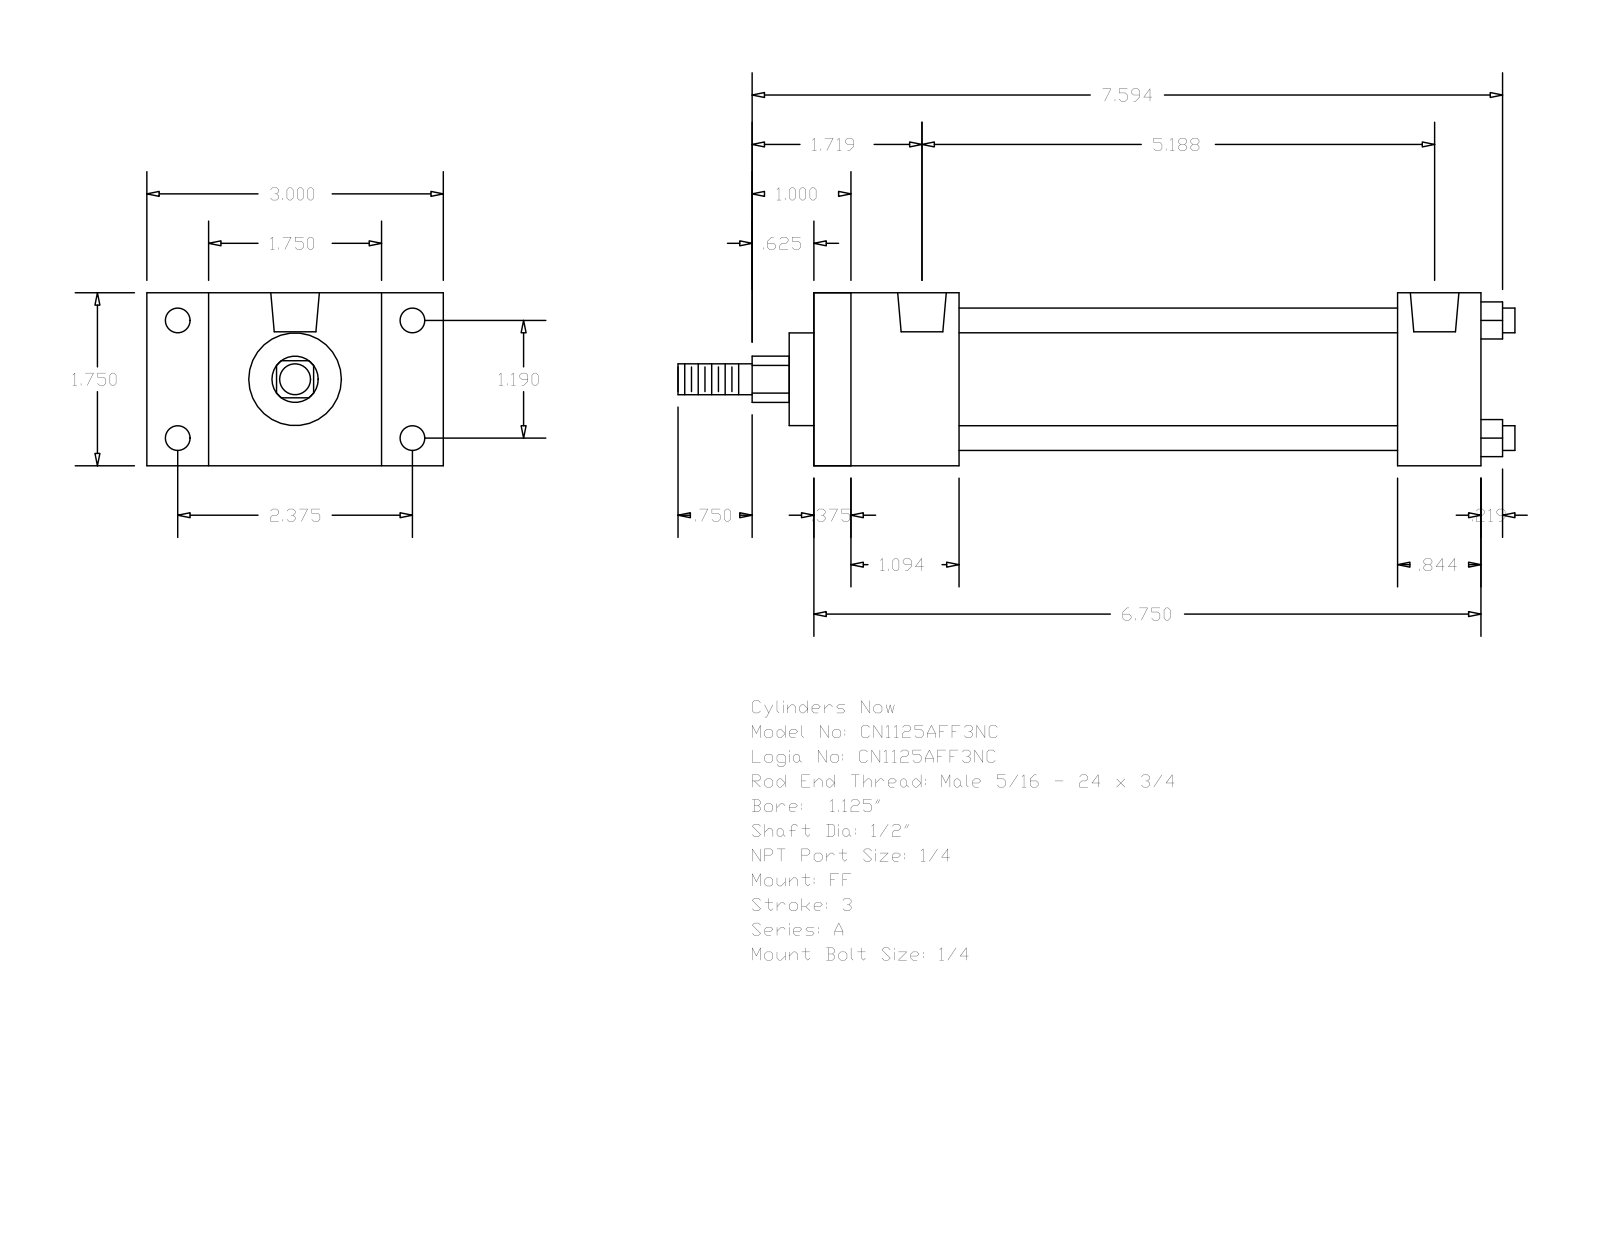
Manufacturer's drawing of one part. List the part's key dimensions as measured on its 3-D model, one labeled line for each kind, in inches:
Part name (STEP PRODUCT): A_FF__0112_0.5
STEP written by: GSSL Pune (CONFIG_CONTROL_DESIGN)
Units: inches
Bodies: 0 solids, 92 faces (64 planar, 28 cylindrical, 0 other)
Overall size (bounding box): 8.469 × 3 × 1.75
Round holes (diameter × count): ⌀0.219 ×4, ⌀0.25 ×4, ⌀0.492 ×2
Round bosses / shafts (diameter × count): ⌀0.25 ×4, ⌀1.255 ×1, ⌀0.937 ×1, ⌀0.5 ×1, ⌀0.313 ×1
Partial cylindrical surfaces — rounded edges, fillets, slot ends (radius × count): R0.234 ×1
Main face-to-face distances: 1.75, 6.75, 0.375, 6.375, 0.625, 5.906, 5.531, 0.844, 1.469, 1.094
Hole centre spacings: 1.19, 2.375, 2.656, 5.063, 0.062, 0.063, 5.125, 5.125
